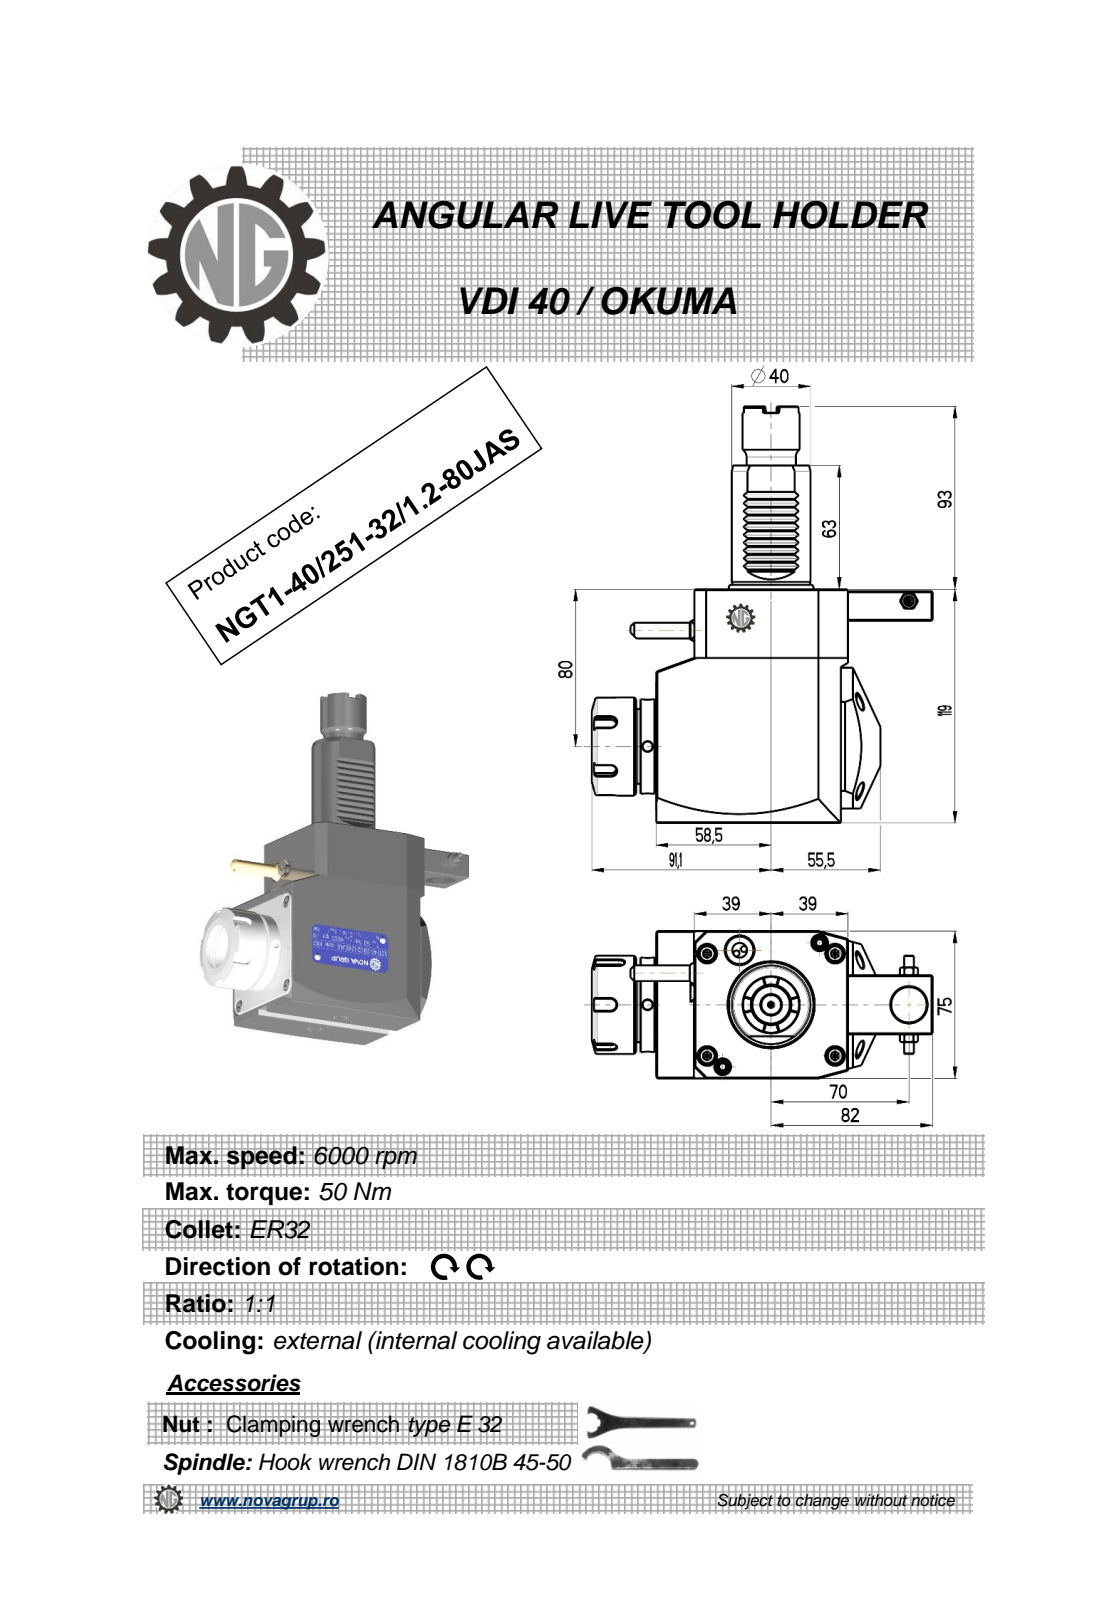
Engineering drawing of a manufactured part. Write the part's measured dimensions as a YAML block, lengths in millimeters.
part_name: "NGT1_40_251_32_1_2_80JAS"
step_written_by: "PRO/ENGINEER BY PARAMETRIC TECHNOLOGY CORPORATION, 2010280 (CONFIG_CONTROL_DESIGN)"
units: millimeters
bodies: {solids: 1, faces: 490, planar: 223, cylindrical: 100, other: 167}
overall_size: [212, 173.1, 76.6]
volume: 1000000
surface_area: 79954
round_holes:
  - {diameter: 5, count: 3}
  - {diameter: 3, count: 1}
  - {diameter: 4.2, count: 1}
  - {diameter: 9.5, count: 1}
  - {diameter: 18, count: 1}
  - {diameter: 27, count: 1}
round_bosses_or_shafts:
  - {diameter: 50, count: 1}
  - {diameter: 48, count: 1}
  - {diameter: 41.5, count: 1}
  - {diameter: 41, count: 1}
  - {diameter: 40, count: 1}
  - {diameter: 29, count: 1}
  - {diameter: 25, count: 1}
  - {diameter: 10, count: 1}
partial_cylinders:
  - {radius: 0.26, count: 12}
  - {radius: 0.3, count: 10}
  - {radius: 0.2, count: 6}
  - {radius: 3, count: 5}
  - {radius: 5.8, count: 2}
  - {radius: 6, count: 2}
  - {radius: 600, count: 2}
  - {radius: 0.5, count: 1}
face_to_face_distances: [75, 119, 19.5, 97.5, 78, 1, 3.5, 22.5, 20, 114]
hole_center_spacings: [20.93, 61.13, 72.5, 132.75, 151.98]
